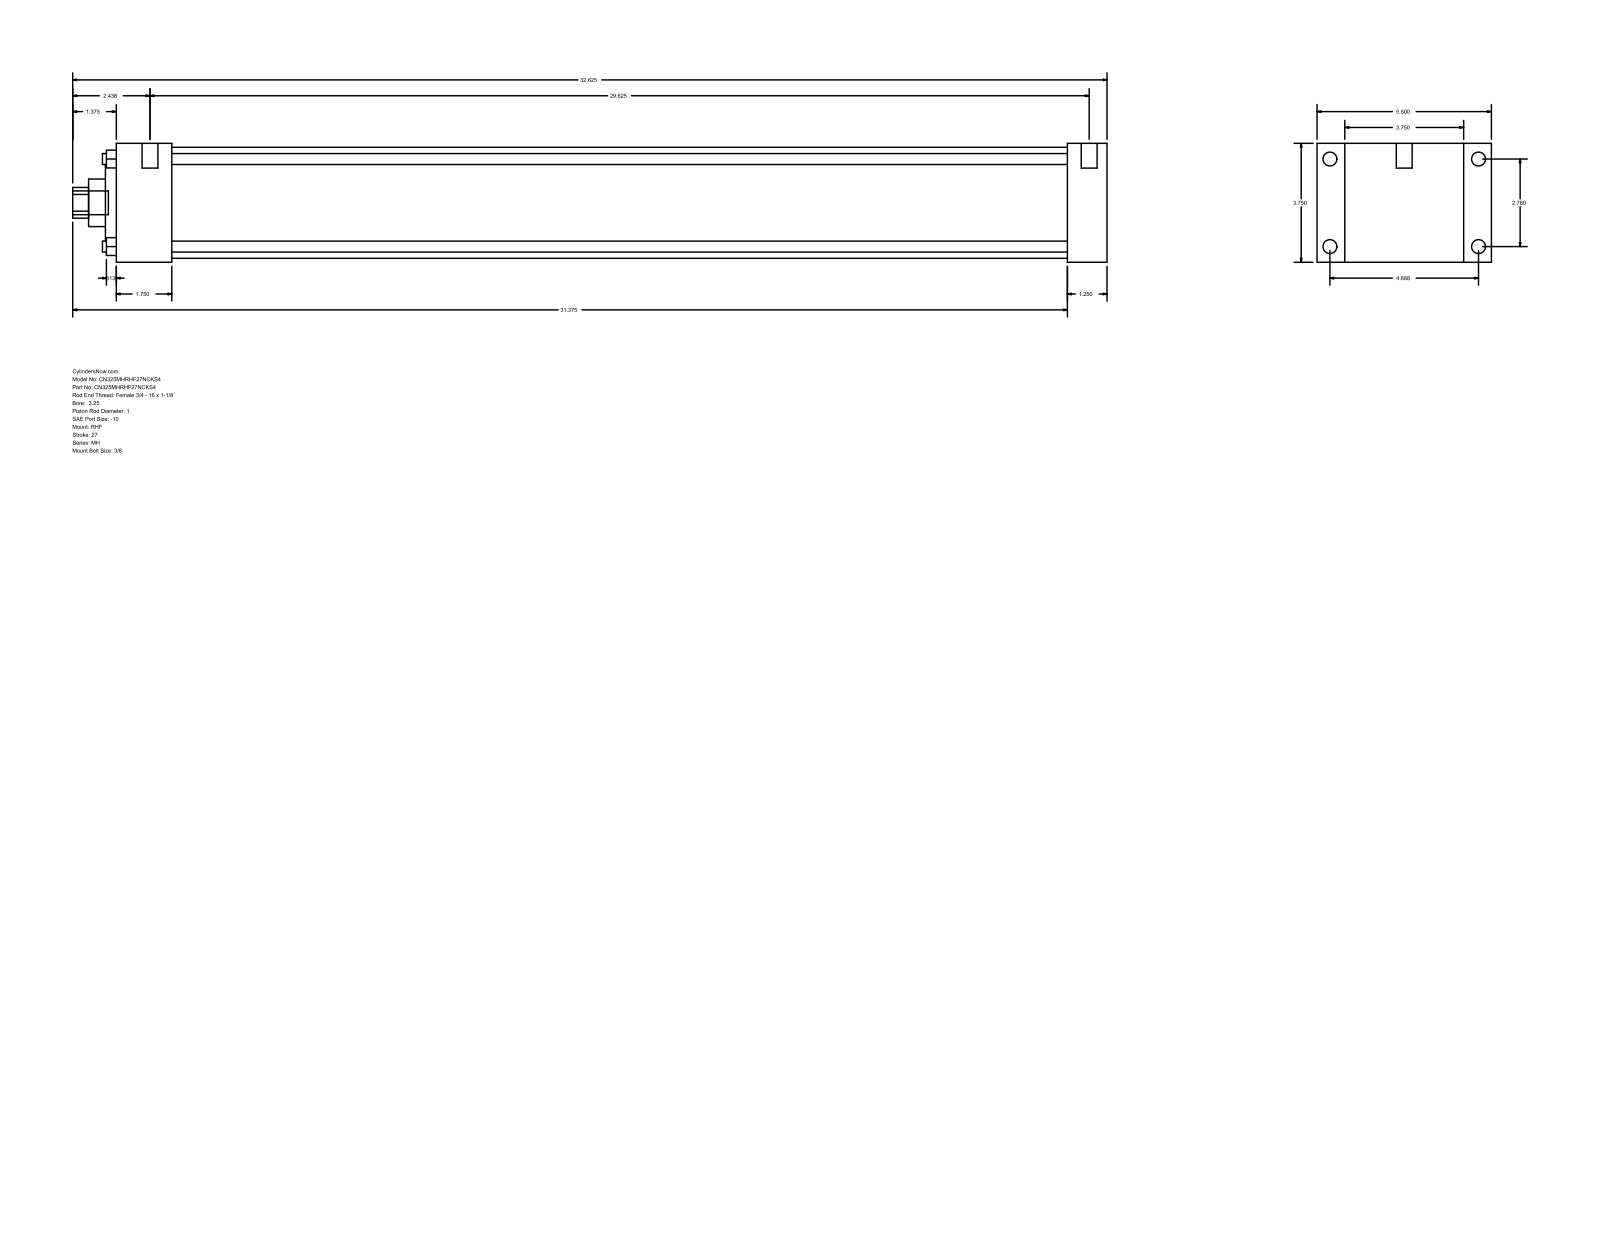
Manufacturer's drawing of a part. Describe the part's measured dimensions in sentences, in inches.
The part is named "MH_RHF__0325_1". Its 3-D file was written by "GSSL Pune (CONFIG_CONTROL_DESIGN)". It is 0 solids with 90 faces: 61 planar, 29 cylindrical and 0 other. Overall it measures 32.625 by 5.5 by 3.75 inches. Round holes: 4 of diameter 0.345, 1 of diameter 1, 1 of diameter 1.5, 1 of diameter 2.375, 1 of diameter 3.5. Round bosses or shafts: 4 of diameter 0.438, 4 of diameter 0.219, 2 of diameter 0.5, 1 of diameter 0.75. Partial cylindrical surfaces (rounded edges, fillets, slot ends): 1 of radius 0.484. The main face-to-face distances are 3.75, 1.25, 0.875, 4.625, 30, 31.25, 5.5, 1.75, 28.25, 29.5. The hole center spacings are 1.952, 2.76, 3.903.
